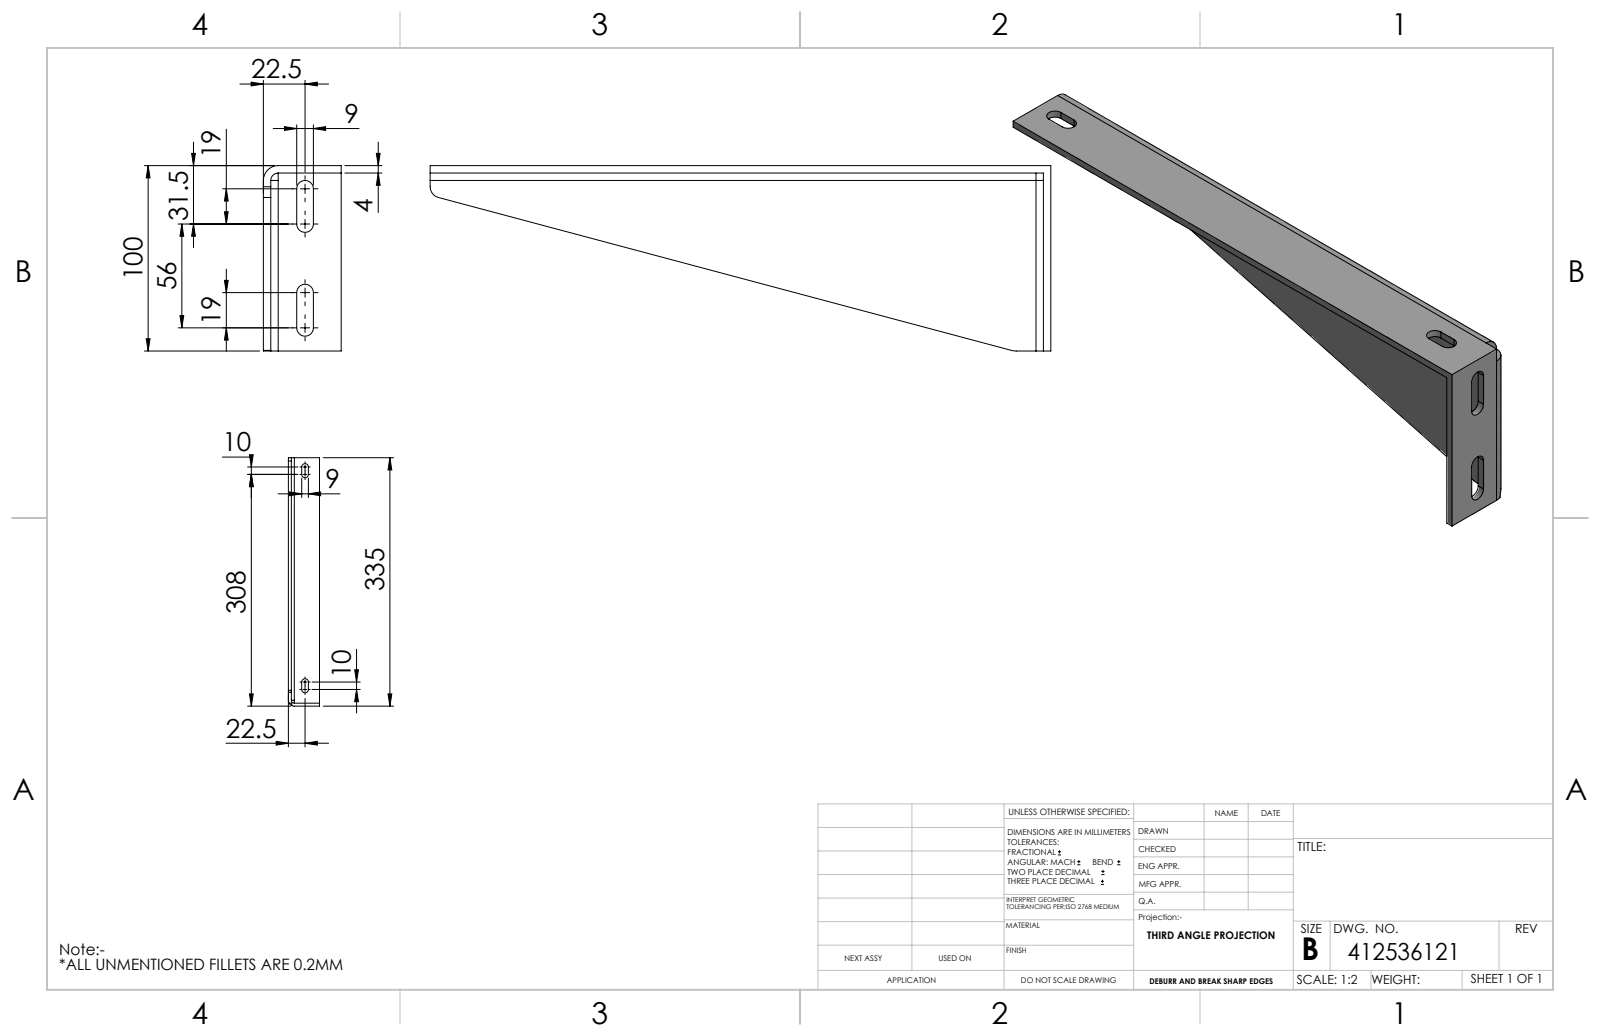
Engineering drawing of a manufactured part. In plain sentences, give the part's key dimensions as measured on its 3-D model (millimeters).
The part is named "412536121 Konsole links l=335". Its 3-D file was written by "Autodesk Inventor 2016 (AUTOMOTIVE_DESIGN)". It is 1 solid with 41 faces: 26 planar, 15 cylindrical and 0 other. Overall it measures 335 by 100 by 42 millimeters. Its volume is 138 687 cubic millimeters and its surface area 73 845 square millimeters. Partial cylindrical surfaces (rounded edges, fillets, slot ends): 9 of radius 4.5, 2 of radius 4, 2 of radius 8, 1 of radius 6, 1 of radius 10. The main face-to-face distances are 4, 42, 38, 18, 27, 14, 23, 9, 24, 15.
